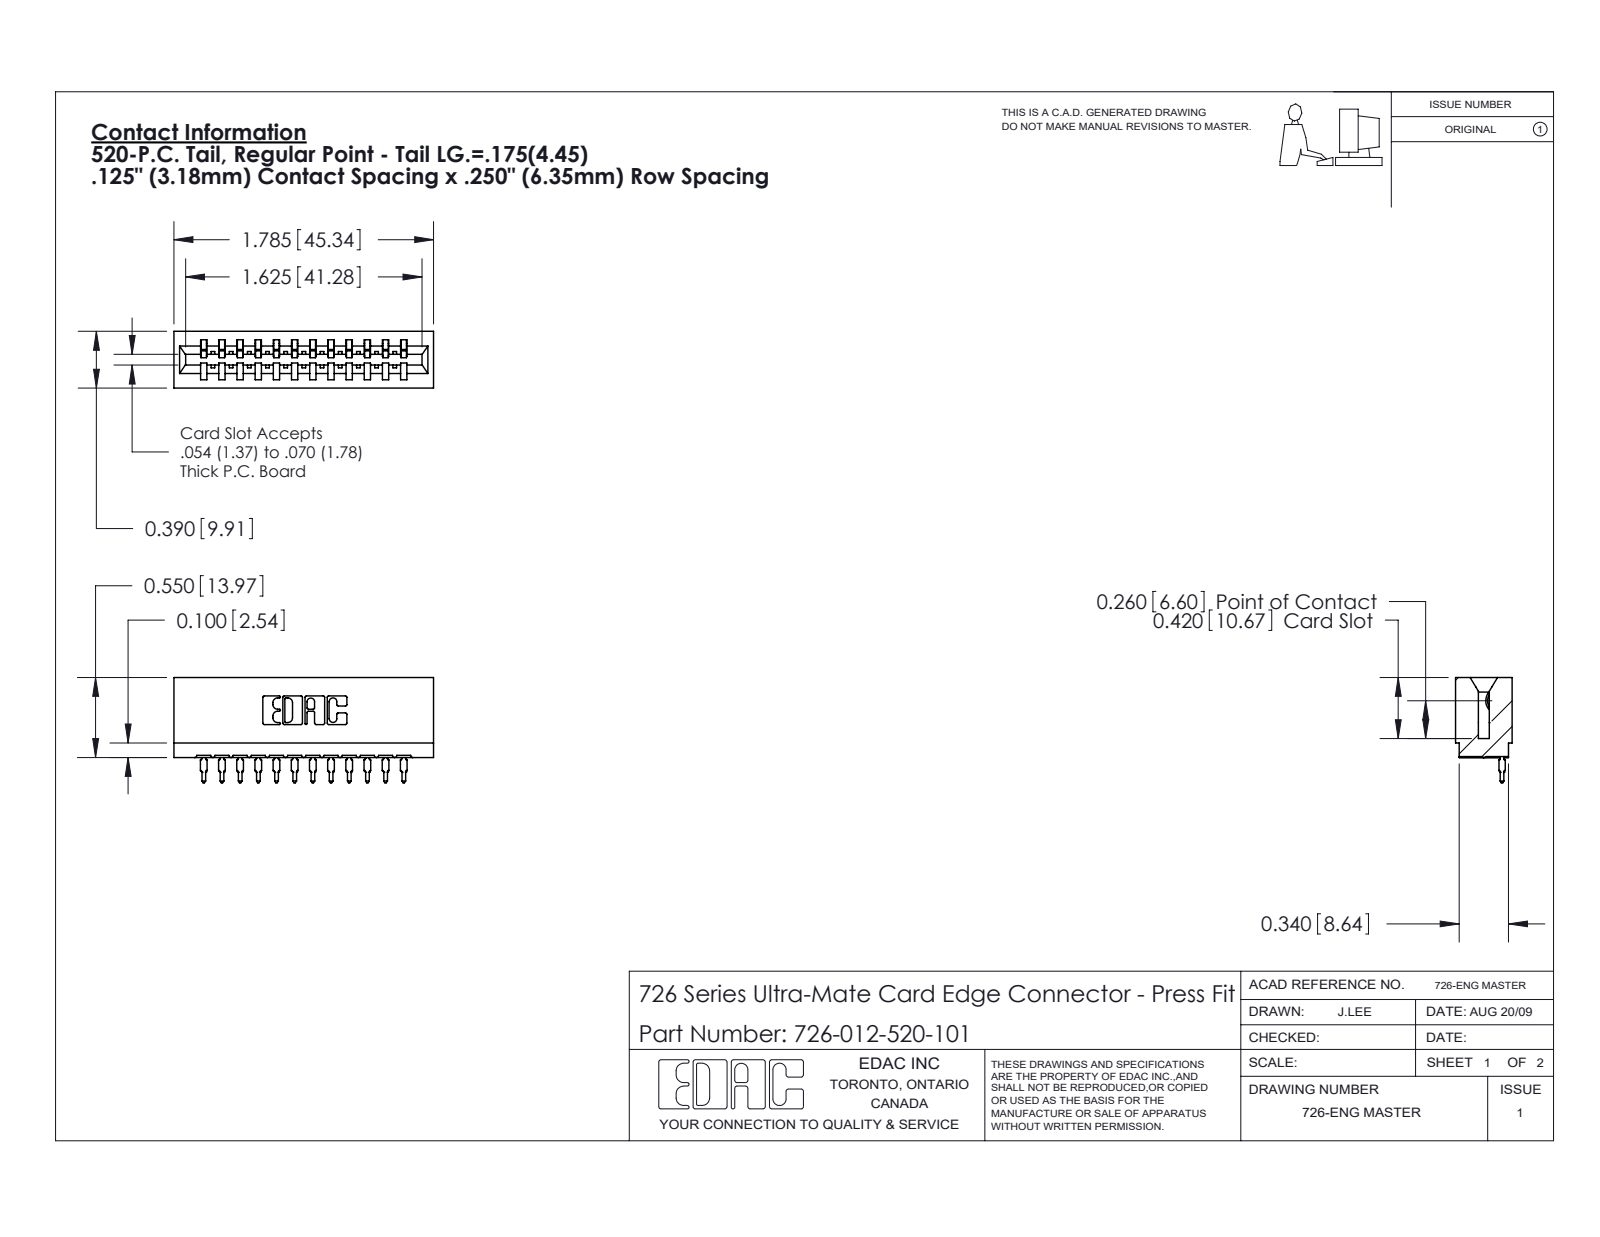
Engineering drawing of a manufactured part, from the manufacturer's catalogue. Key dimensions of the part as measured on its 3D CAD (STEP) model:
Part name (STEP PRODUCT): 726-012-520-101; 726 Part_.515 Slot Depth - 01; 746-292-001_520
STEP written by: SolidWorks 2020 (CONFIG_CONTROL_DESIGN)
Units: inches
Bodies: 13 solids, 1393 faces (811 planar, 270 cylindrical, 312 other)
Overall size (bounding box): 1.785 × 0.724 × 0.39
Volume: 0.256 in³ · Surface area: 9.126 in²
Partial cylindrical surfaces — rounded edges, fillets, slot ends (radius × count): R0.021 ×24, R0.01 ×22, R0.015 ×13, R0.007 ×6, R0.031 ×6, R0.005 ×4, R0.011 ×4, R0.026 ×3
Main face-to-face distances: 0.25, 0.333, 0.057, 0.5, 0.39, 0.125, 0.75, 0.125, 0.292, 0.042
